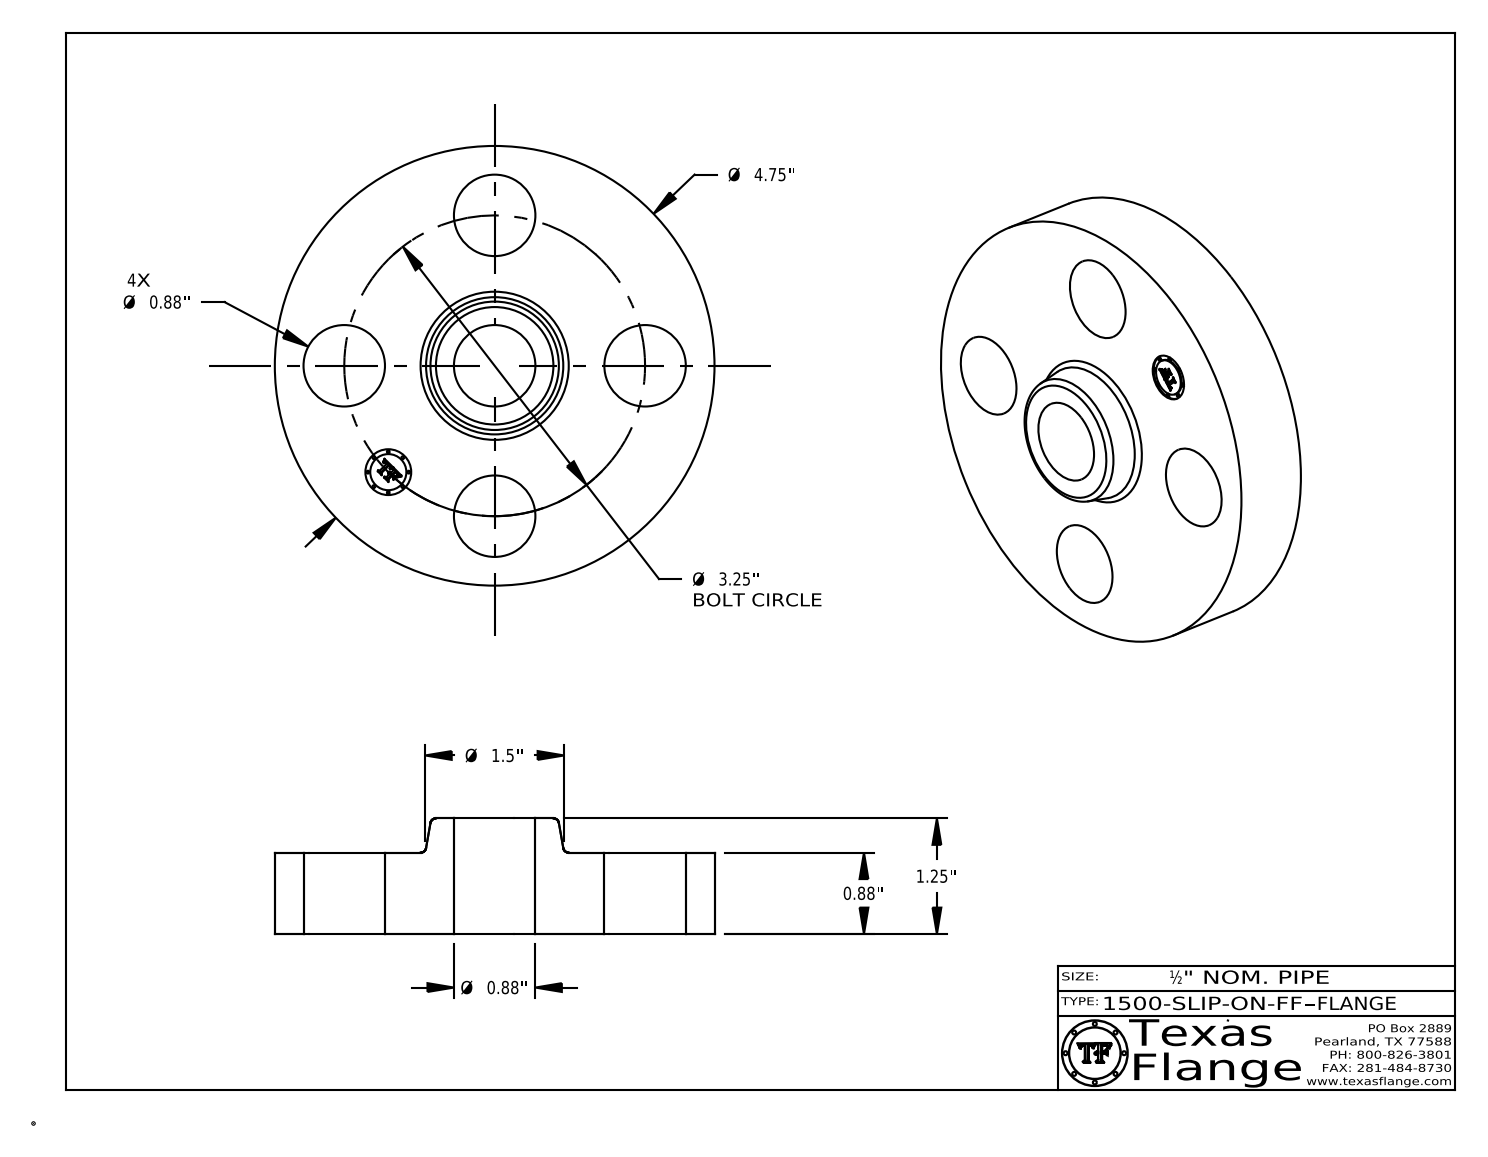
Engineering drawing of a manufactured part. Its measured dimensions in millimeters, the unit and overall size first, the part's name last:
Units: millimetres
Overall size (bounding box): 120.7 × 120.7 × 31.8
Round holes (diameter × count): ⌀22.4 ×5, ⌀12.6 ×1
Round bosses / shafts (diameter × count): ⌀0.8 ×8, ⌀120.7 ×1, ⌀9.9 ×1
Main face-to-face distances: 22.4, 31.8, 9.4, 22, 0.4, 9.8, 3.8, 3.7, 0.7, 2.4
Hole centre spacings: 41.3, 58.4, 31.6, 76.3, 82.6
Volume: 217 800 mm³ · Surface area: 36 790 mm²
Bodies: 1 solid, 406 faces (368 planar, 32 cylindrical, 6 other)
Part name (STEP PRODUCT): 1500-SLIP-ON-FF
STEP written by: CATIA V5 STEP AP214 (AUTOMOTIVE_DESIGN)
